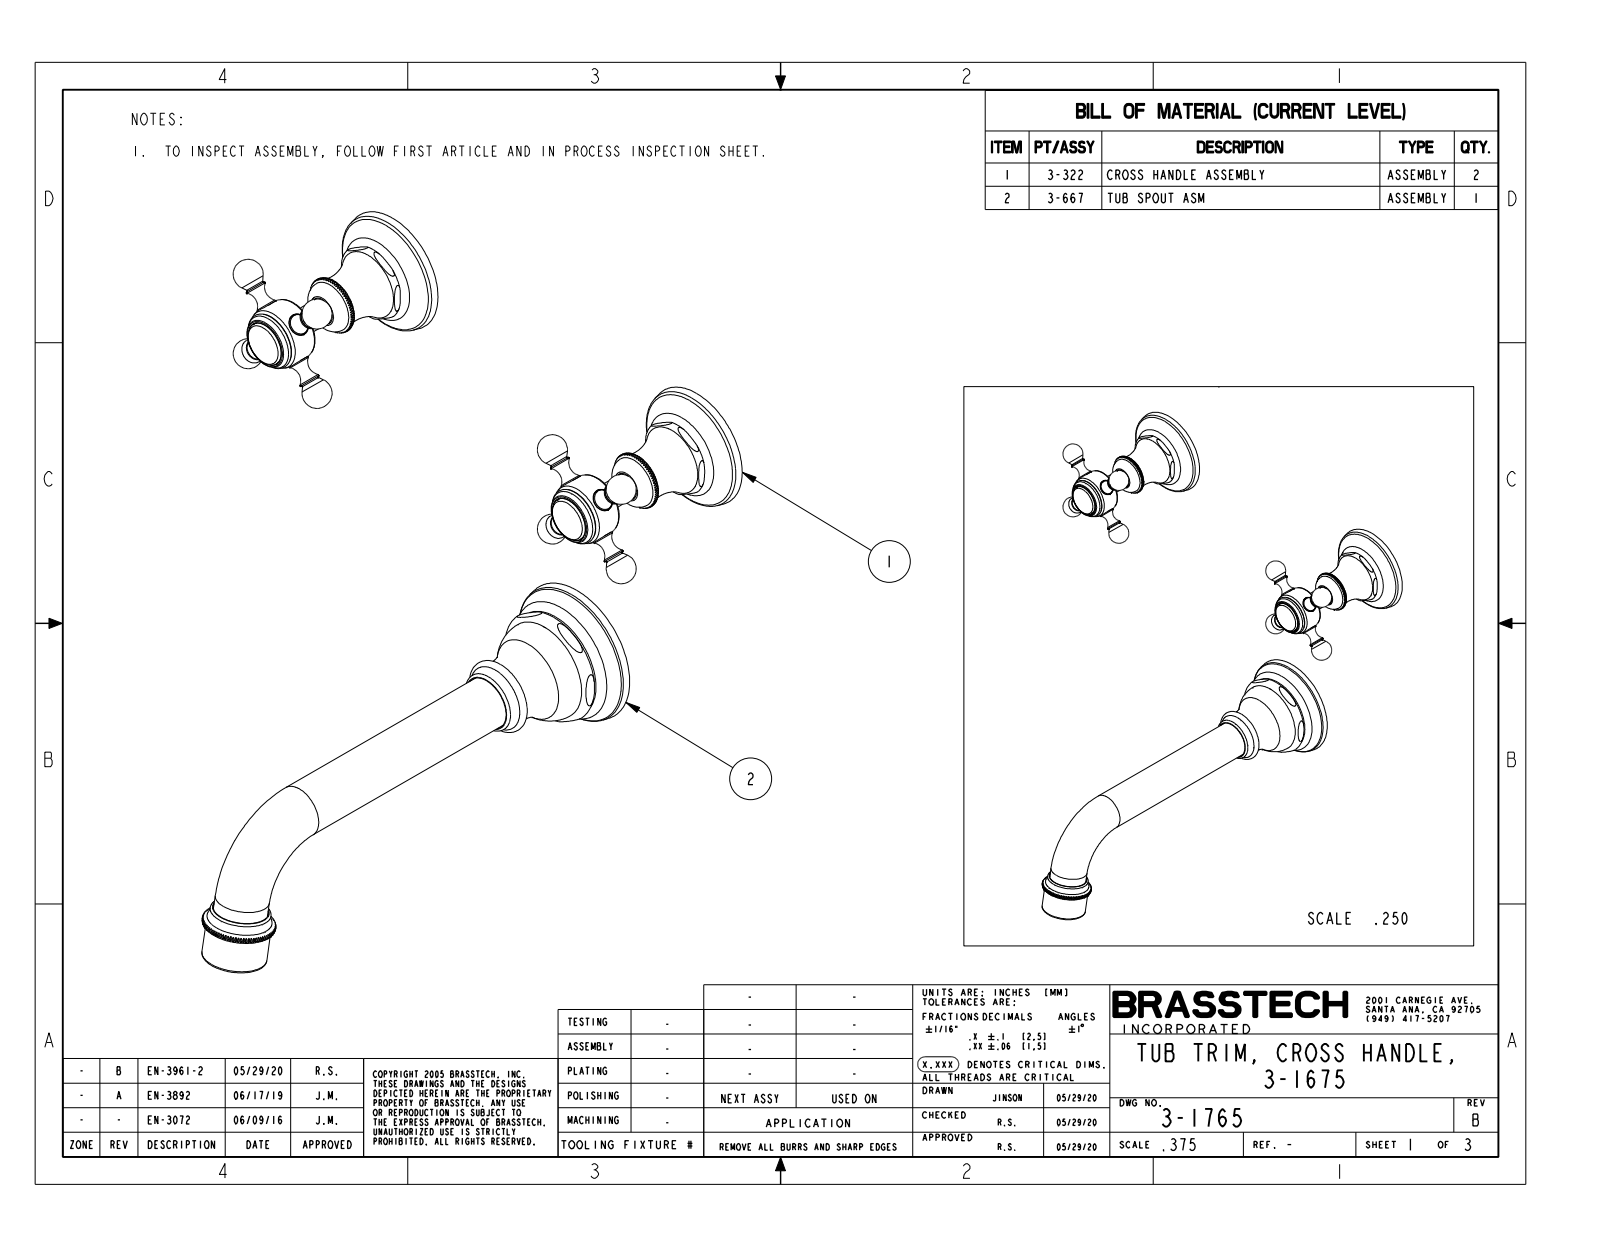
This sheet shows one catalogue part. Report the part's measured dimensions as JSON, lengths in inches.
{"part_name": "3-1765_SW0002", "step_written_by": "CREO PARAMETRIC BY PTC INC, 2018400 (AUTOMOTIVE_DESIGN)", "units": "inches", "bodies": {"solids": 3, "faces": 774, "planar": 512, "cylindrical": 58, "other": 204}, "overall_size": [10.728, 10.24, 9.455], "volume_in3": 21.27, "surface_area_in2": 100.8, "round_holes": [[0.41, 8], [0.201, 6]], "round_bosses_or_shafts": [[0.392, 8], [1, 2], [0.5, 2], [1.2, 1]], "face_to_face_distances": [0.84, 3.38, 2.54, 2.1, 1.375, 1.375, 5.568, 4.14, 3.3, 0.76], "hole_center_spacings": [5.569]}
